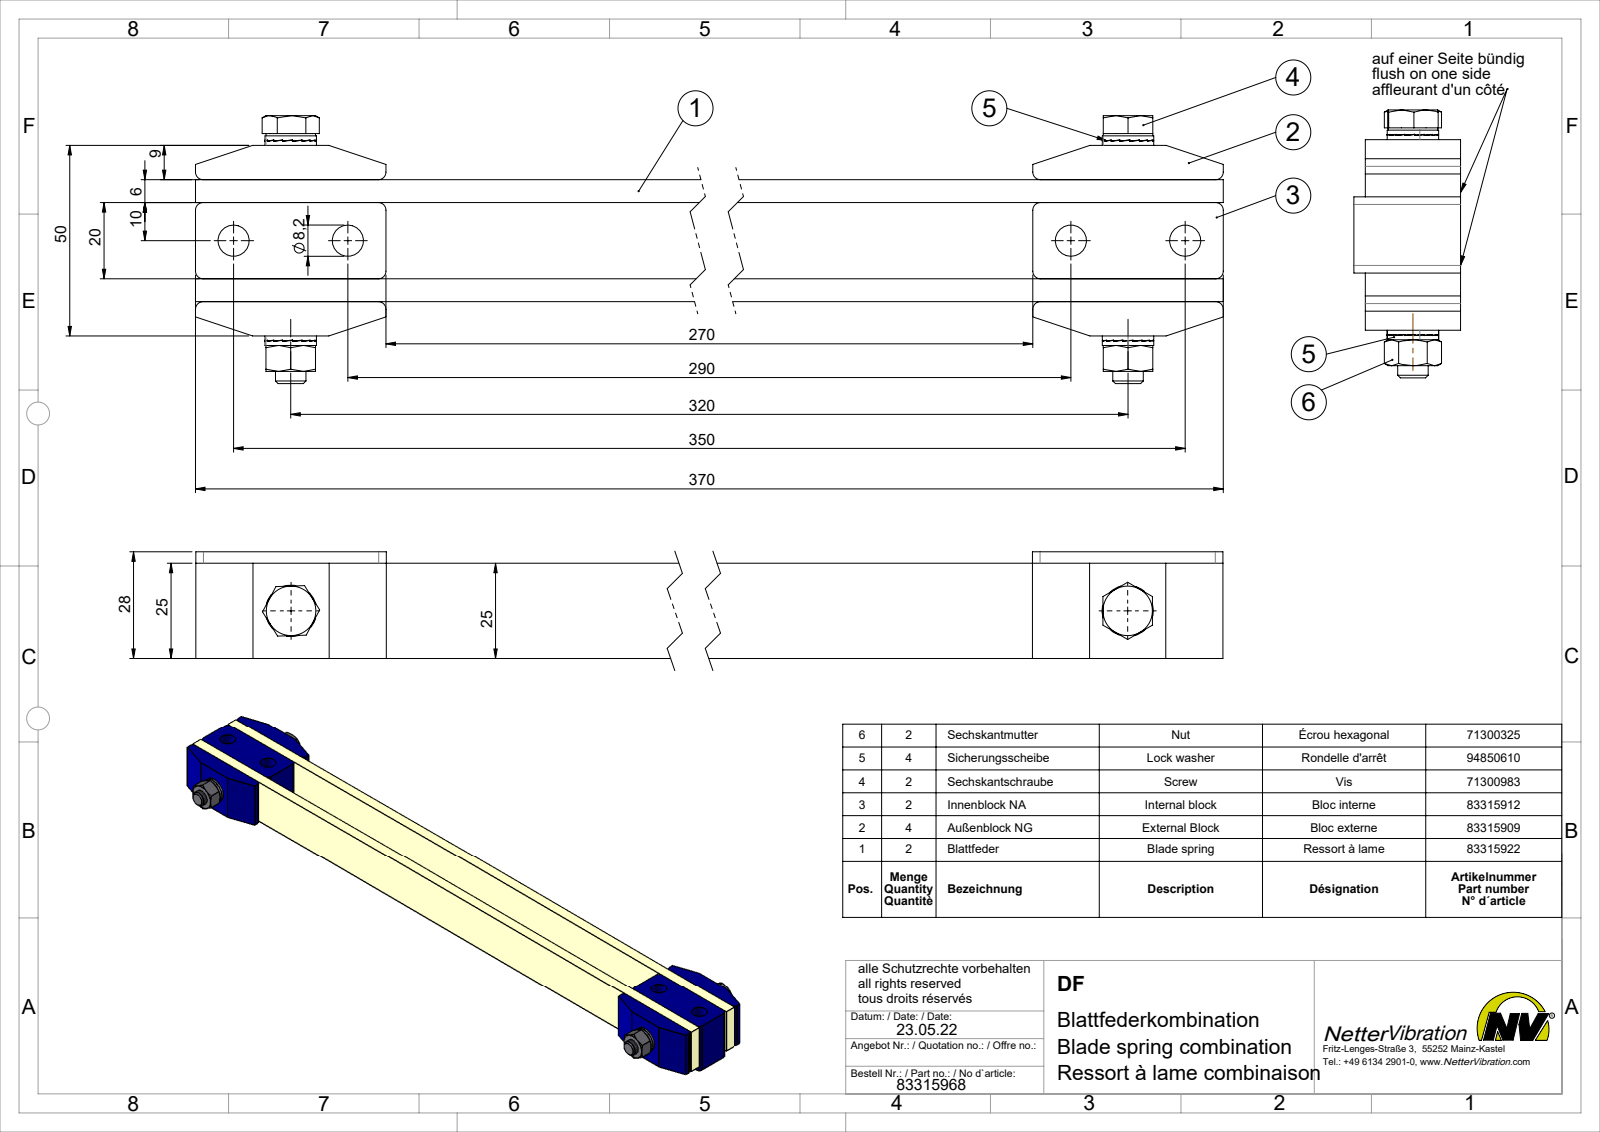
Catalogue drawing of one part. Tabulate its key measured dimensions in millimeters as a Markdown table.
| quantity | value |
| --- | --- |
| part name | Blattfederkombination DF # 83315968 |
| STEP written by | SolidWorks 2015 (AUTOMOTIVE_DESIGN) |
| units | millimeters |
| bodies | 16 solids, 694 faces (558 planar, 84 cylindrical, 52 other) |
| overall size | 370 × 70.3 × 28 |
| volume | 203 207 mm³ |
| surface area | 82 981 mm² |
| round holes (diameter × count) | 8.2 × 6, 6.8 × 2, 8 × 2, 8.5 × 2, 8.7 × 2 |
| round bosses / shafts (diameter × count) | 13.5 × 2, 13 × 2 |
| partial cylindrical surfaces (radius × count) | 2 × 16 |
| main face-to-face distances | 6, 26, 20, 32, 25, 50, 9, 15, 35, 41 |
| hole center spacings | 320, 30, 290, 350 |
